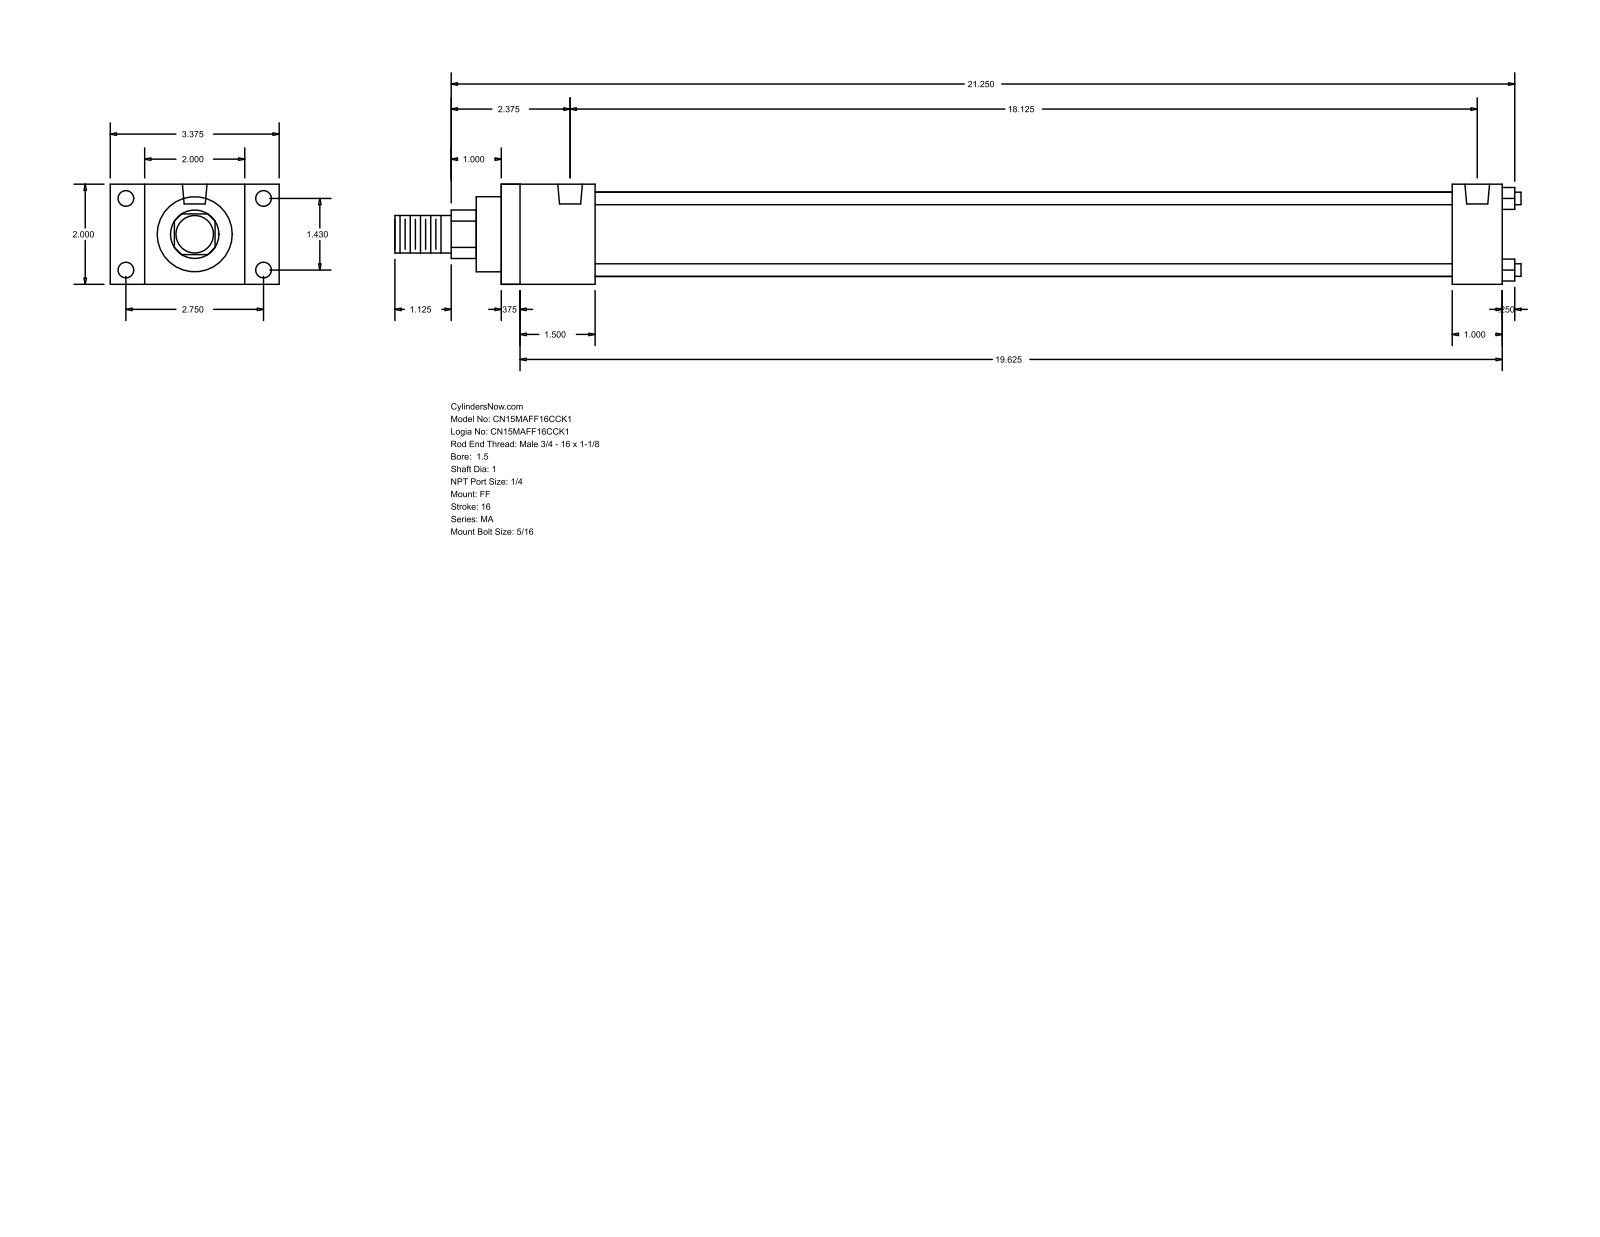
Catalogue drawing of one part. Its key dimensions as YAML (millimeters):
part_name: "MA_FF__0150_1"
step_written_by: "GSSL Pune (CONFIG_CONTROL_DESIGN)"
units: millimeters
bodies: {solids: 0, faces: 92, planar: 64, cylindrical: 28, other: 0}
overall_size: [571.5, 85.72, 50.8]
round_holes:
  - {diameter: 7.94, count: 8}
  - {diameter: 12.49, count: 2}
round_bosses_or_shafts:
  - {diameter: 6.35, count: 4}
  - {diameter: 42.93, count: 1}
  - {diameter: 38.1, count: 1}
  - {diameter: 25.4, count: 1}
  - {diameter: 19.05, count: 1}
partial_cylinders:
  - {radius: 12.29, count: 1}
face_to_face_distances: [50.8, 508, 9.52, 498.48, 25.4, 47.63, 482.6, 38.11, 473.08, 434.97]
hole_center_spacings: [36.32, 69.84, 78.72, 460.37]
